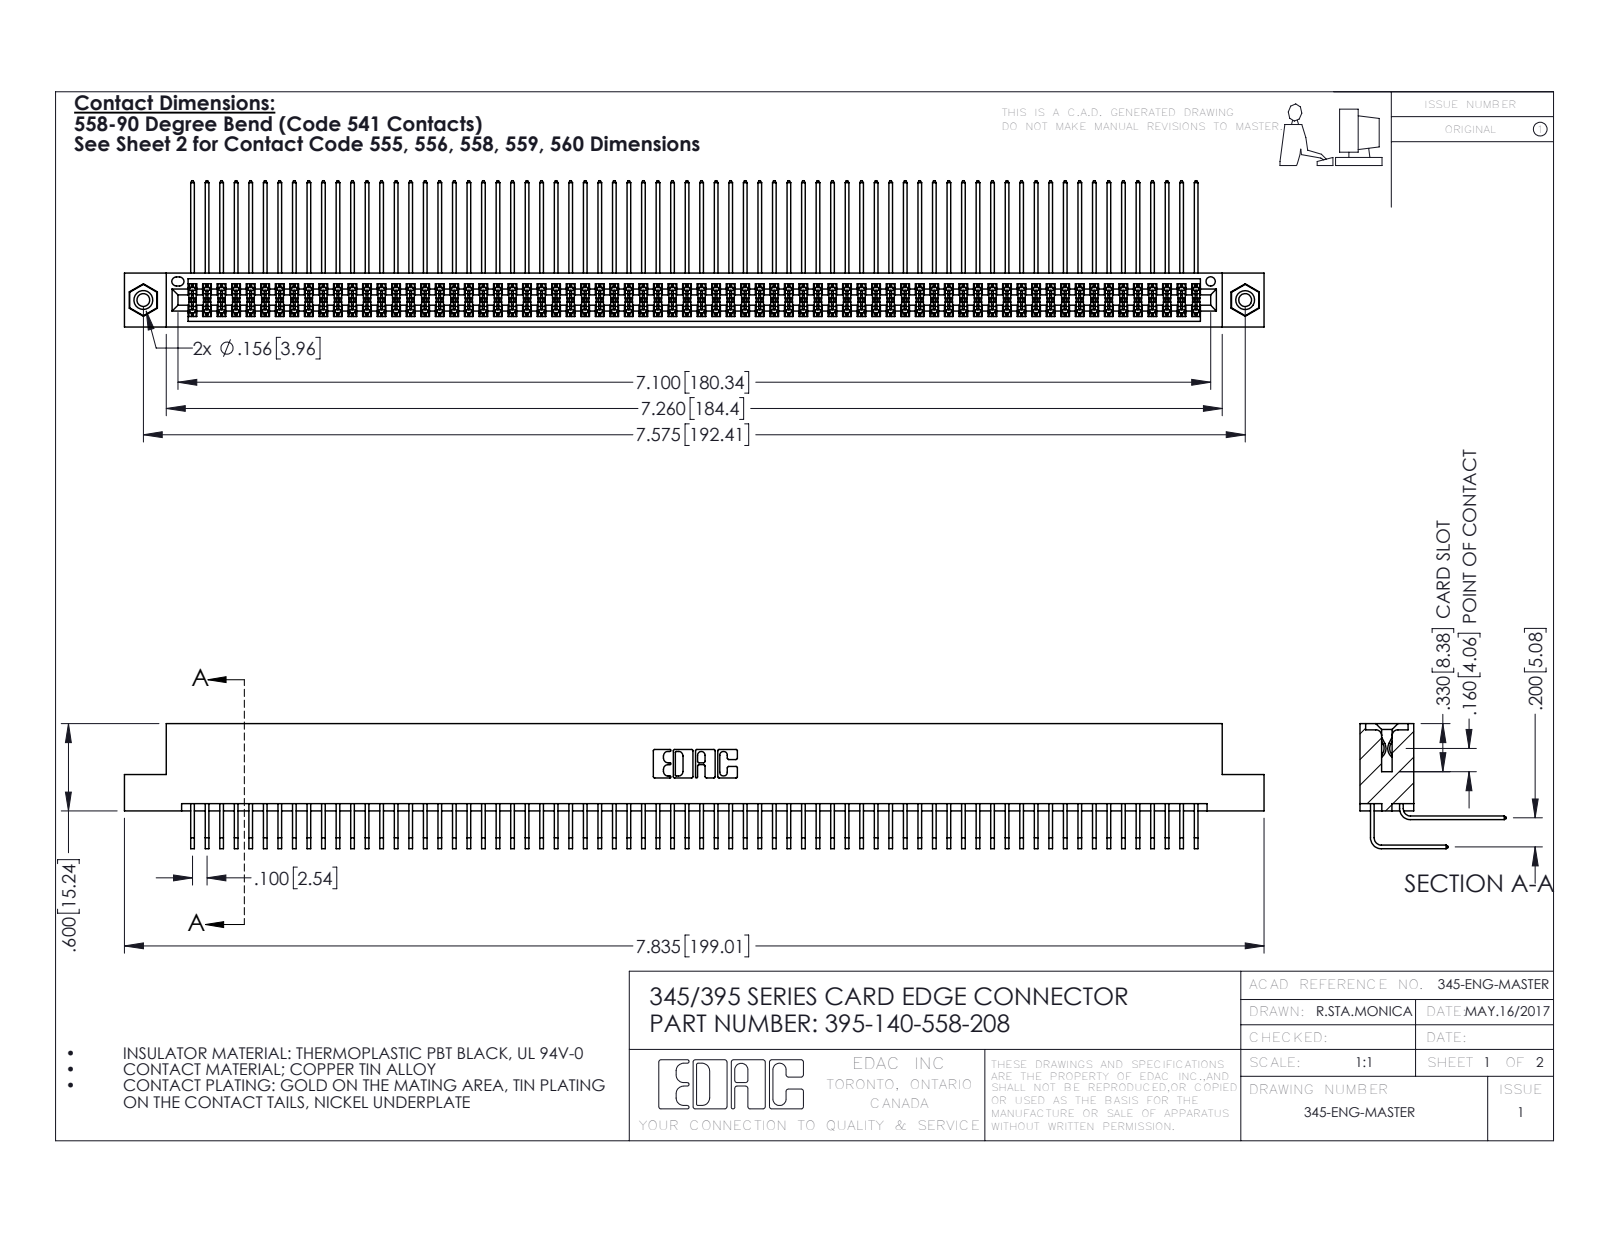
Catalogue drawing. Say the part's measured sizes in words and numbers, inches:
The part is named "345-250-001_345-250-003-102; 345-292-001_558 Tail - 2; 395-140-558-208; 345 Part_Flush Mounting Lugs - 0.156 Dia-TI (+1 more)". Its 3-D file was written by "SolidWorks 2016 (CONFIG_CONTROL_DESIGN)". It is 143 solids with 7466 faces: 5012 planar, 2438 cylindrical and 16 other. Overall it measures 7.835 by 1.005 by 0.859 inches. Its volume is 1.244 cubic inches and its surface area 53.47 square inches. Round holes: 2 of diameter 0.089, 2 of diameter 0.125, 2 of diameter 0.156, 1 of diameter 0.064. Round bosses or shafts: 2 of diameter 0.155. Partial cylindrical surfaces (rounded edges, fillets, slot ends): 279 of radius 0.006, 22 of radius 0.01, 6 of radius 0.007, 6 of radius 0.031, 3 of radius 0.026, 2 of radius 0.014, 2 of radius 0.019, 2 of radius 0.022. The main face-to-face distances are 0.072, 0.298, 0.2, 0.37, 0.098, 0.272, 0.025, 0.225, 0.025, 0.175. The hole center spacings are 0.27, 7.339, 7.575.
